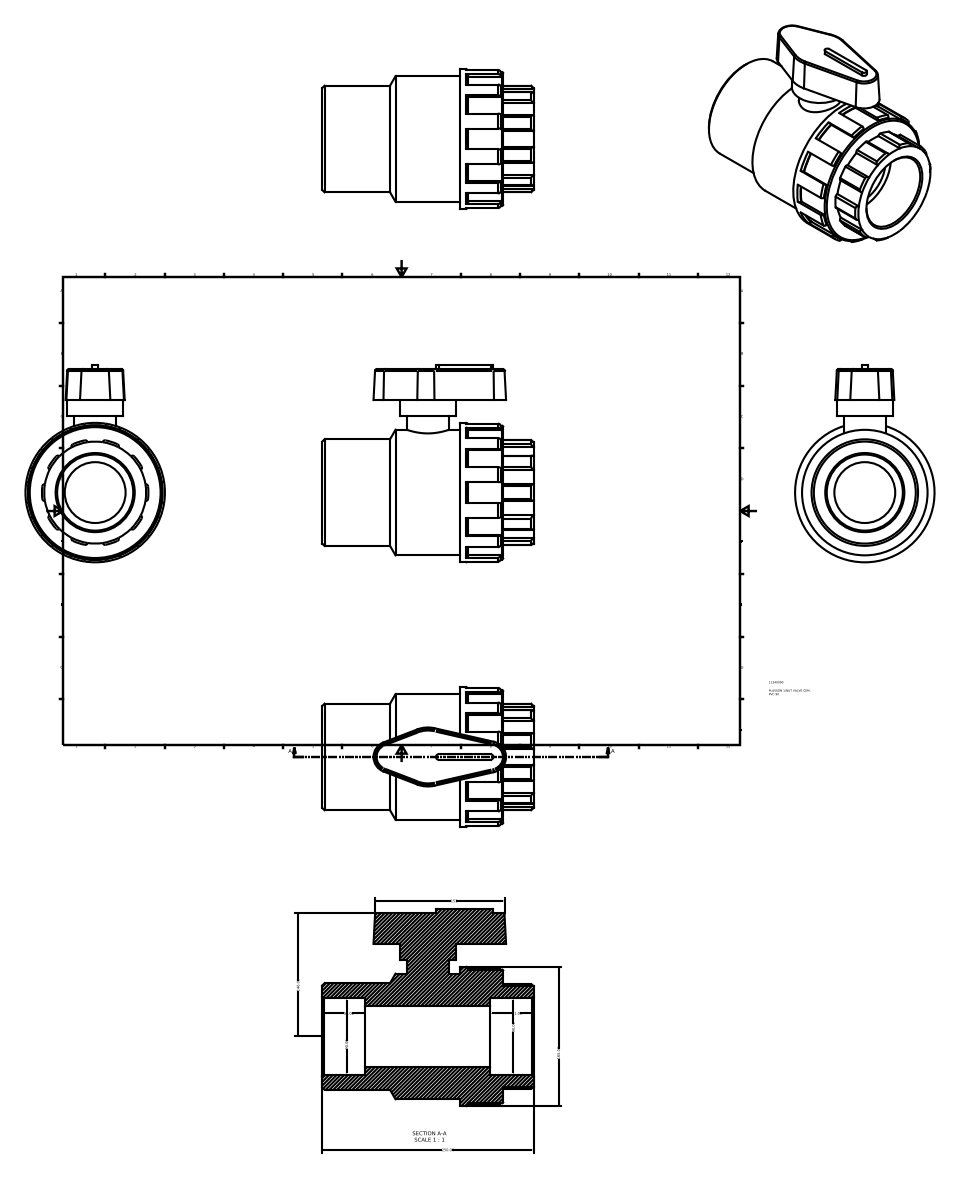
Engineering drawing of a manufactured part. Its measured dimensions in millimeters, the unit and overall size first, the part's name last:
Units: millimetres
Overall size (bounding box): 250 × 232.88 × 165
Round holes (diameter × count): ⌀72 ×1, ⌀90 ×1
Round bosses / shafts (diameter × count): ⌀165 ×1, ⌀158.4 ×1, ⌀148.5 ×1, ⌀126 ×1, ⌀66 ×1, ⌀49.5 ×1
Partial cylindrical surfaces — rounded edges, fillets, slot ends (radius × count): R2.7 ×20, R1.8 ×4, R3.3 ×2, R60.3 ×1
Main face-to-face distances: 51, 35.7, 163.3, 199, 214.3, 250, 36.5, 86.7, 15.3, 112.3
Volume: 3 010 000 mm³ · Surface area: 238 136 mm²
Bodies: 1 solid, 166 faces (64 planar, 55 cylindrical, 47 other)
Part name (STEP PRODUCT): 11340090
STEP written by: Autodesk Inventor 2015 (AUTOMOTIVE_DESIGN)
